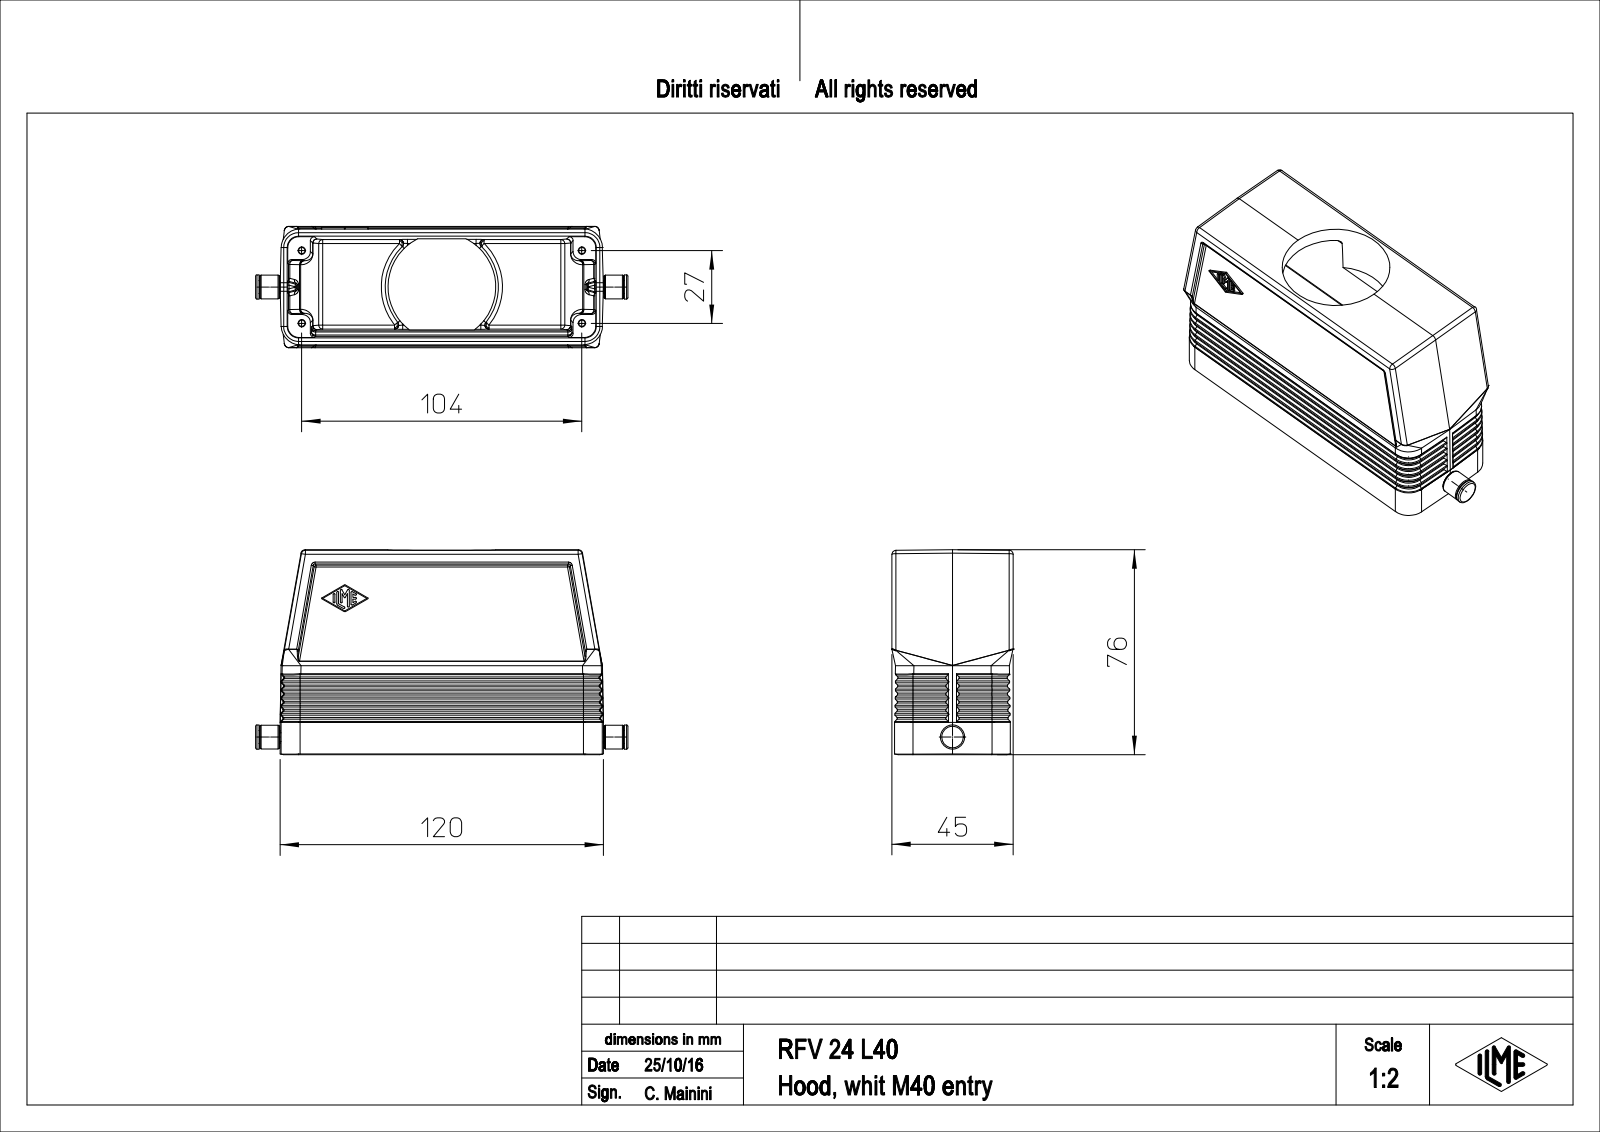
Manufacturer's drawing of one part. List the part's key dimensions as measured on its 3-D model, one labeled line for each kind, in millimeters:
Part name (STEP PRODUCT): RFV_24_L40
STEP written by: PTC Creo Elements/Direct Modeling 19.0E 27-Jun-2016 (C) Parametric Technology GmbH (AUTOMOTIVE_DESIGN)
Units: millimetres
Bodies: 1 solid, 529 faces (220 planar, 149 cylindrical, 160 other)
Overall size (bounding box): 138.2 × 76 × 45
Volume: 102 848 mm³ · Surface area: 53 838 mm²
Round holes (diameter × count): ⌀2.75 ×4, ⌀40 ×1
Round bosses / shafts (diameter × count): ⌀9 ×1, ⌀8.8 ×1, ⌀4.8 ×1, ⌀3.2 ×1
Partial cylindrical surfaces — rounded edges, fillets, slot ends (radius × count): R0.5 ×78, R1.5 ×11, R7 ×8, R3 ×4, R4.2 ×4, R21 ×1
Main face-to-face distances: 43, 2.01, 2, 4, 44, 1, 8.45, 6, 6.01, 4.01
Hole centre spacings: 53.72, 27, 104, 107.45
